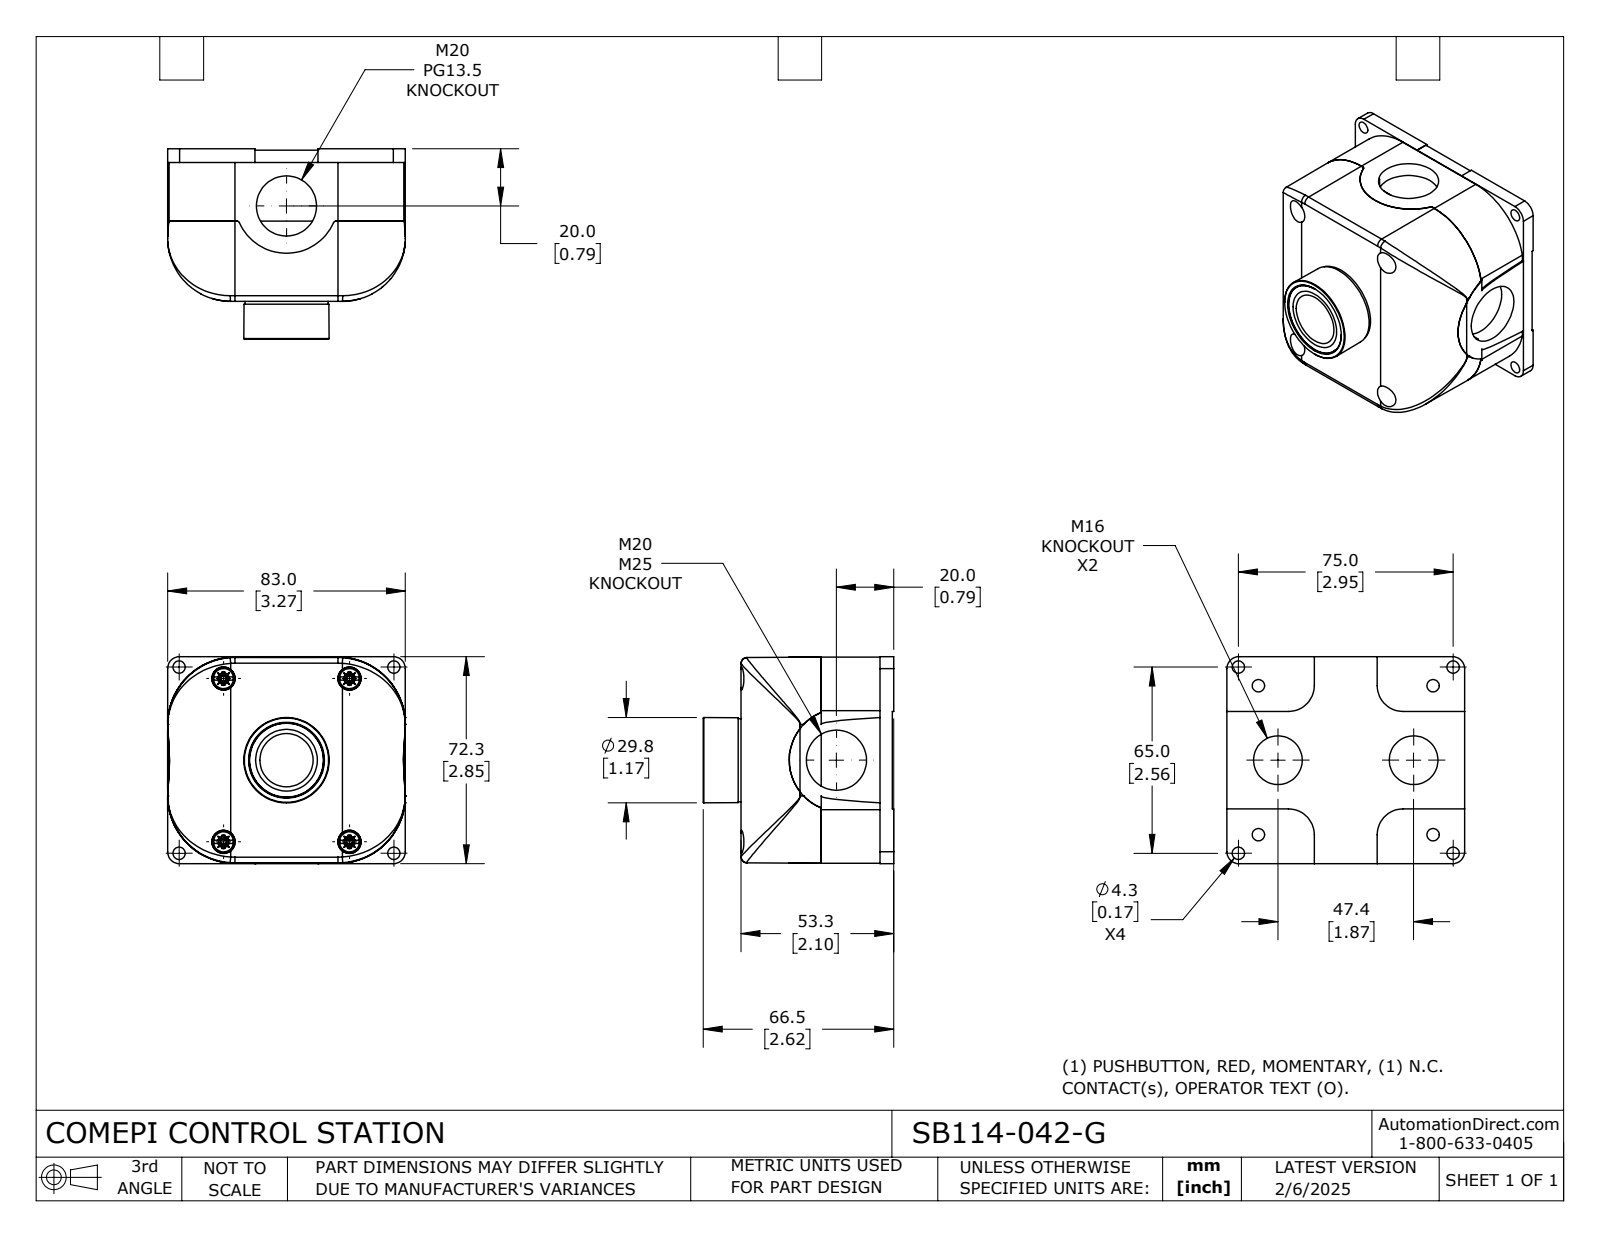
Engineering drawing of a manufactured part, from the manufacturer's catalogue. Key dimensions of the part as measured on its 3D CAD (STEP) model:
Part name (STEP PRODUCT): SB114-042-G
STEP written by: SolidWorks 2024 (CONFIG_CONTROL_DESIGN)
Units: inches
Bodies: 4 solids, 548 faces (300 planar, 144 cylindrical, 104 other)
Overall size (bounding box): 3.268 × 2.846 × 2.618
Volume: 12.8 in³ · Surface area: 89.33 in²
Round holes (diameter × count): ⌀0.169 ×8, ⌀0.323 ×4, ⌀0.669 ×2, ⌀0.827 ×2, ⌀0.531 ×1, ⌀0.713 ×1, ⌀0.854 ×1
Round bosses / shafts (diameter × count): ⌀0.276 ×4, ⌀1.142 ×1, ⌀1.016 ×1, ⌀0.748 ×1, ⌀0.728 ×1, ⌀0.63 ×1, ⌀0.614 ×1, ⌀0.61 ×1
Partial cylindrical surfaces — rounded edges, fillets, slot ends (radius × count): R0.035 ×4, R0.079 ×4, R0.354 ×4, R0.38 ×4, R0.925 ×4, R0.008 ×2, R0.01 ×2, R0.709 ×2
Main face-to-face distances: 0.976, 0.098, 0.878, 2.079, 1.98, 1.102, 0.118, 2.098, 0.02, 0.996
Hole centre spacings: 0.376, 1.058, 1.39, 1.578, 1.954, 2.32, 2.367, 2.689
